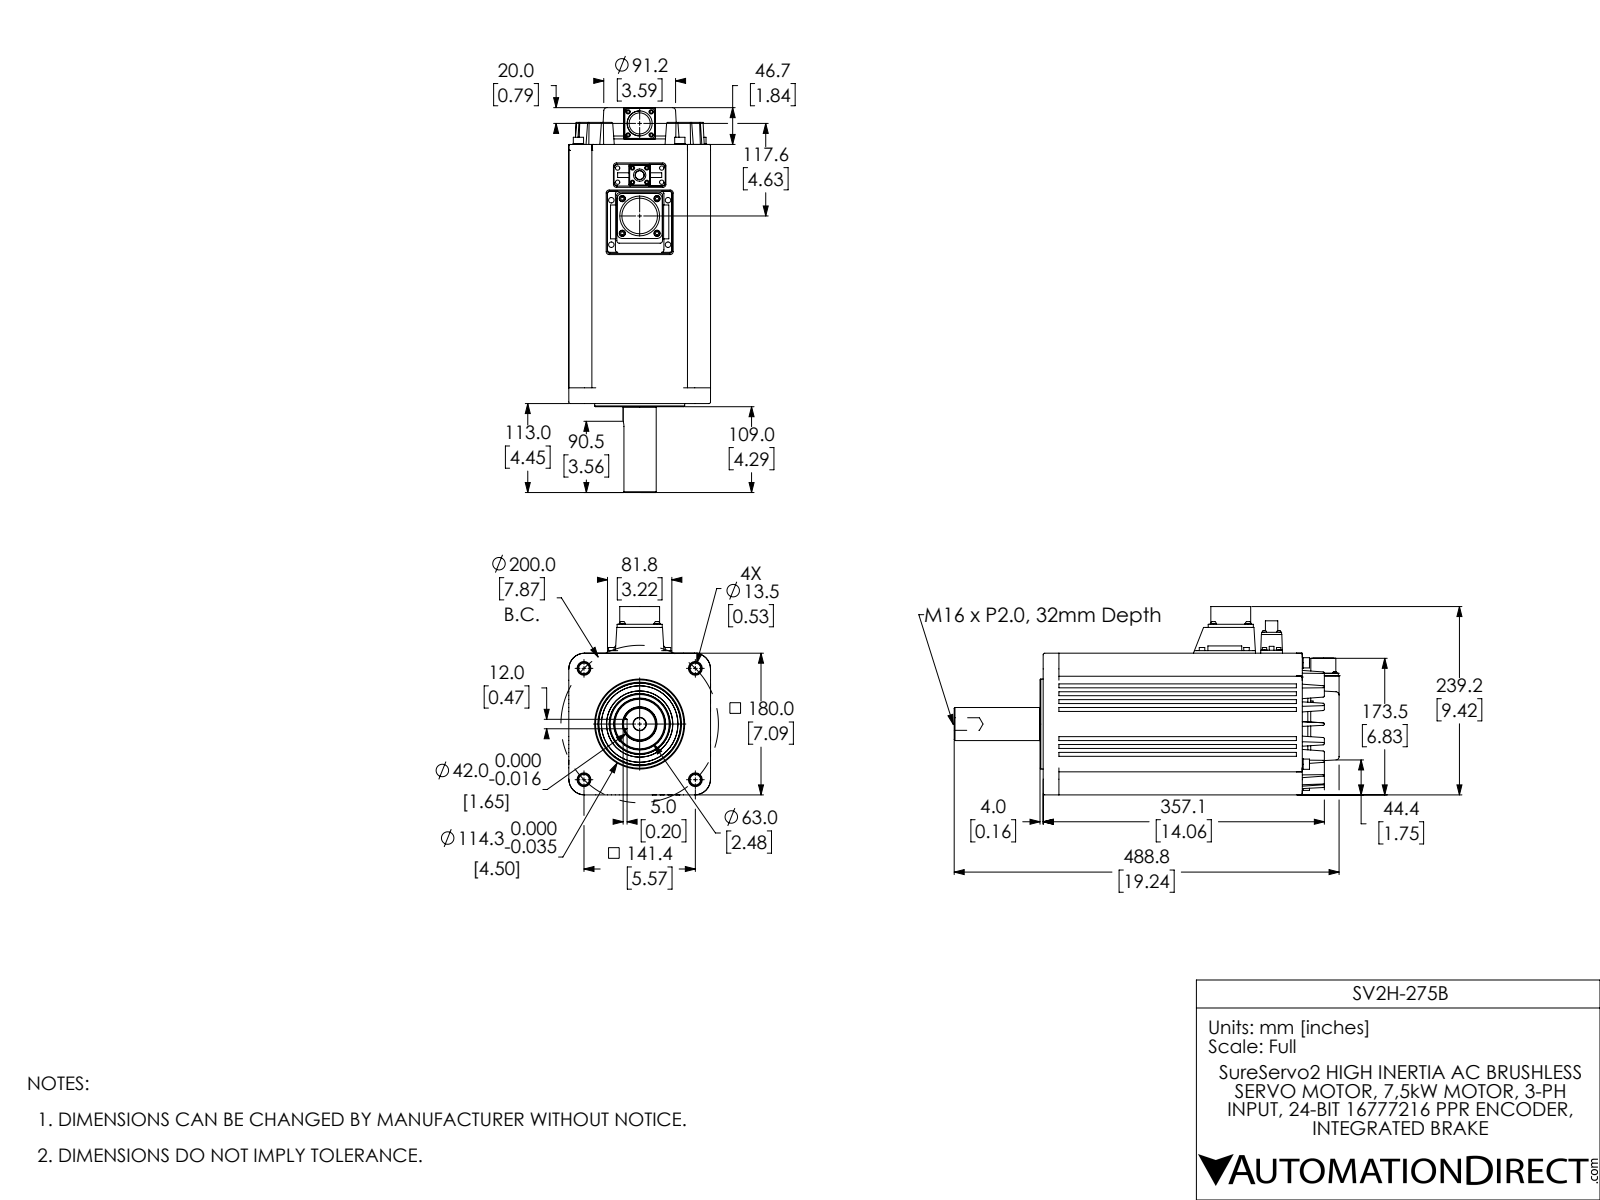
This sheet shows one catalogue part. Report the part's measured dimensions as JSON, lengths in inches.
{"part_name": "SV2H-275B", "step_written_by": "SolidWorks 2017 (AUTOMOTIVE_DESIGN)", "units": "inches", "bodies": {"solids": 1, "faces": 665, "planar": 341, "cylindrical": 219, "other": 105}, "overall_size": [19.244, 9.417, 7.087], "volume_in3": 621.4, "surface_area_in2": 719.3, "round_holes": [[0.315, 2], [0.461, 1], [0.63, 1], [1.058, 1], [1.783, 1], [2.48, 1]], "round_bosses_or_shafts": [[0.217, 7], [0.528, 4], [0.512, 4], [0.315, 4], [0.276, 4], [0.236, 4], [4.567, 1], [4.5, 1]], "partial_cylinders_radius": [[0.064, 16], [0.197, 16], [0.039, 12], [0.118, 12], [0.02, 8], [0.079, 8], [0.15, 8], [0.157, 8]], "face_to_face_distances": [0.197, 7.087, 0.394, 1.154, 0.591, 5.933, 3.031, 3.228, 2.835, 0.787], "hole_center_spacings": [3.661, 2.041, 2.587, 4.628, 7.323]}
